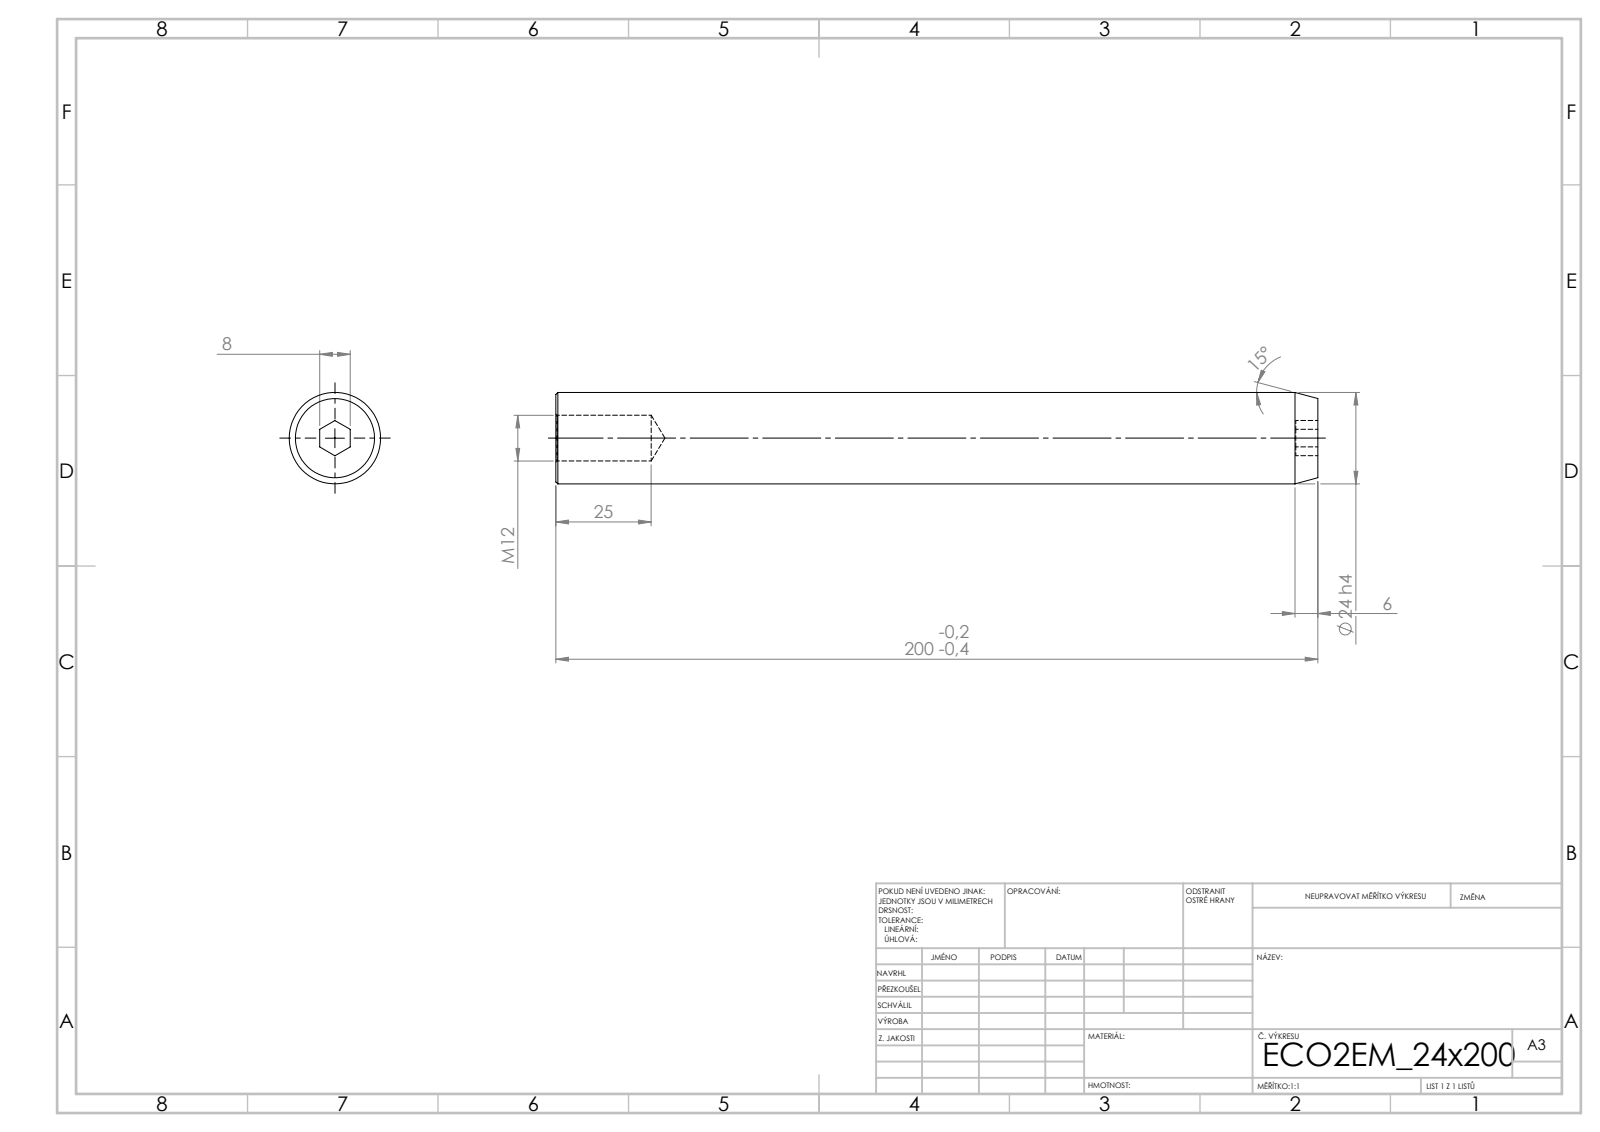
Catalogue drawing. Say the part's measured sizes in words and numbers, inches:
Its 3-D file was written by "SolidWorks 2019 (CONFIG_CONTROL_DESIGN)". It is 1 solid with 21 faces: 9 planar, 4 cylindrical and 8 other. Overall it measures 7.874 by 0.945 by 0.945 inches. Its volume is 5.299 cubic inches and its surface area 26.27 square inches. Round holes: 1 of diameter 0.472. Round bosses or shafts: 1 of diameter 0.945. The main face-to-face distances are 7.874, 0.315, 0.228, 7.646.
